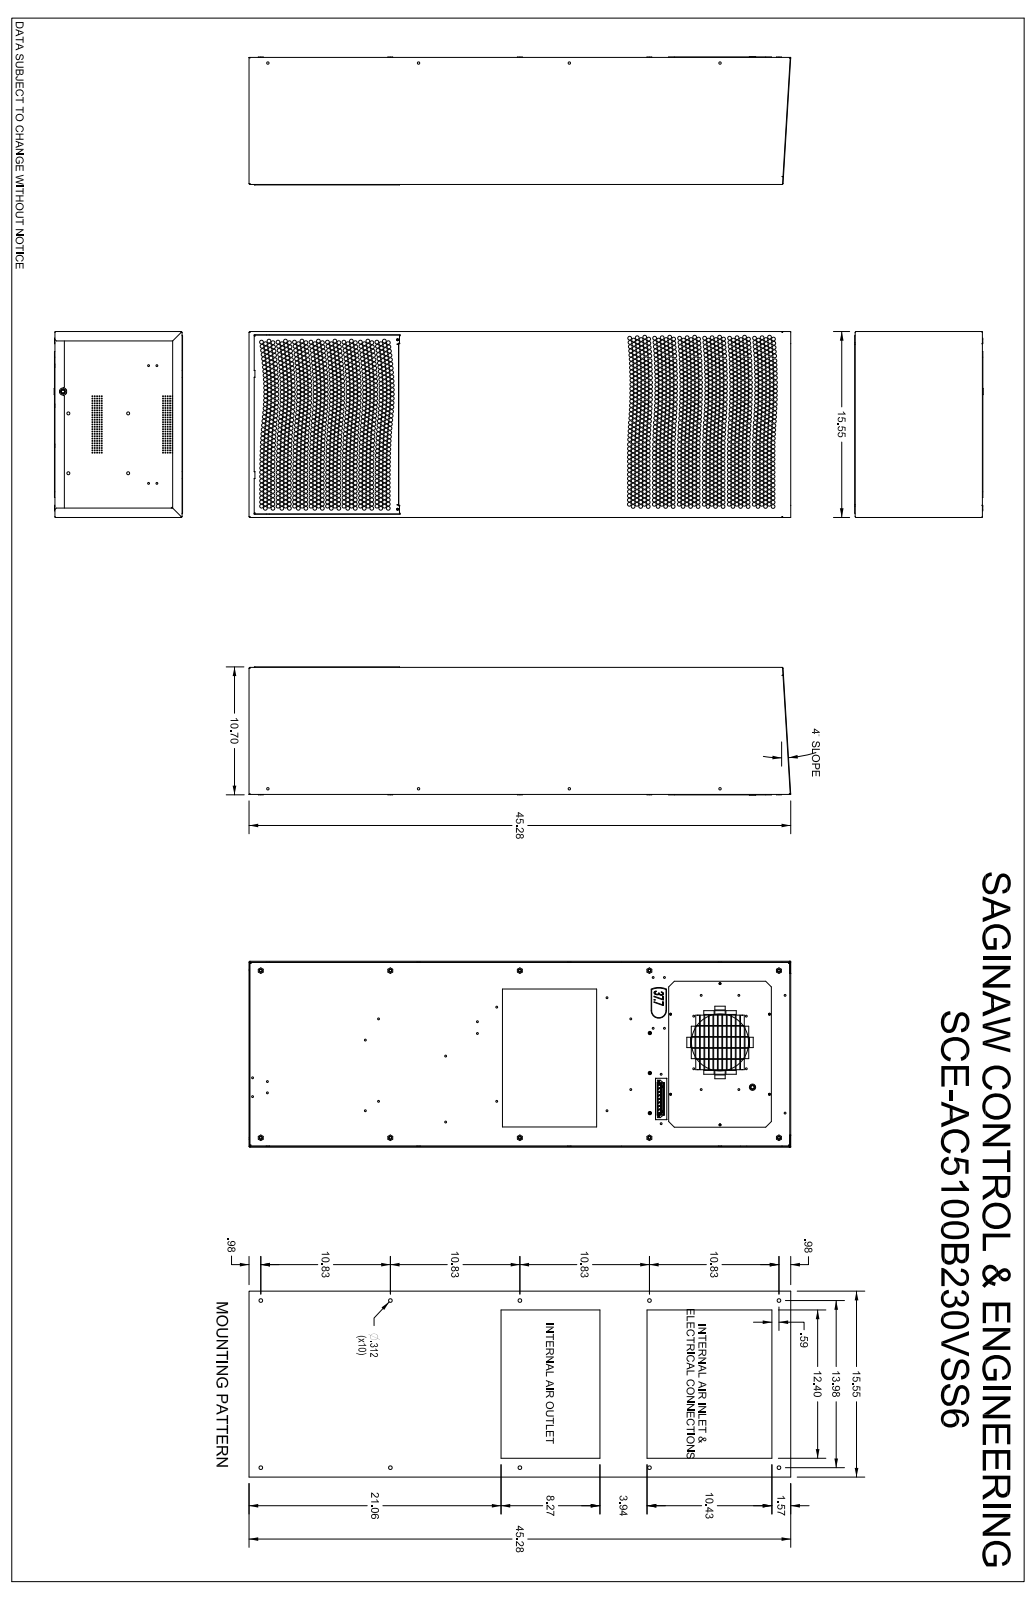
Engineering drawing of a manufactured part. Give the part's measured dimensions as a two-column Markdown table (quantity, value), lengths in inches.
| quantity | value |
| --- | --- |
| part name | SCE-AC5100B120V-2 |
| STEP written by | SolidWorks 2021 (AUTOMOTIVE_DESIGN) |
| units | inches |
| bodies | 44 solids, 2856 faces (2010 planar, 697 cylindrical, 149 other) |
| overall size | 45.281 × 15.551 × 10.732 |
| volume | 175.2 in³ |
| surface area | 7 180 in² |
| round holes (diameter × count) | 0.079 × 250, 0.169 × 67, 0.315 × 58, 0.177 × 21, 0.142 × 11, 0.217 × 10, 0.264 × 10, 0.165 × 9, 0.197 × 5, 0.126 × 4, 0.193 × 4, 0.256 × 4 |
| round bosses / shafts (diameter × count) | 0.276 × 15, 0.236 × 15, 0.11 × 9, 0.325 × 4, 0.528 × 2, 0.429 × 2, 6.693 × 1, 0.472 × 1 |
| partial cylindrical surfaces (radius × count) | 0.079 × 25, 0.008 × 24, 0.039 × 21, 0.012 × 16, 0.118 × 11, 0.018 × 8, 0.02 × 6, 0.059 × 6 |
| main face-to-face distances | 0.039, 0.098, 15.413, 0.059, 15.512, 10.591, 0.138, 15.374, 15.453, 15.315 |
| hole center spacings | 0.197, 0.591, 0.394, 1.181, 0.787, 0.984, 1.378, 1.575 |
